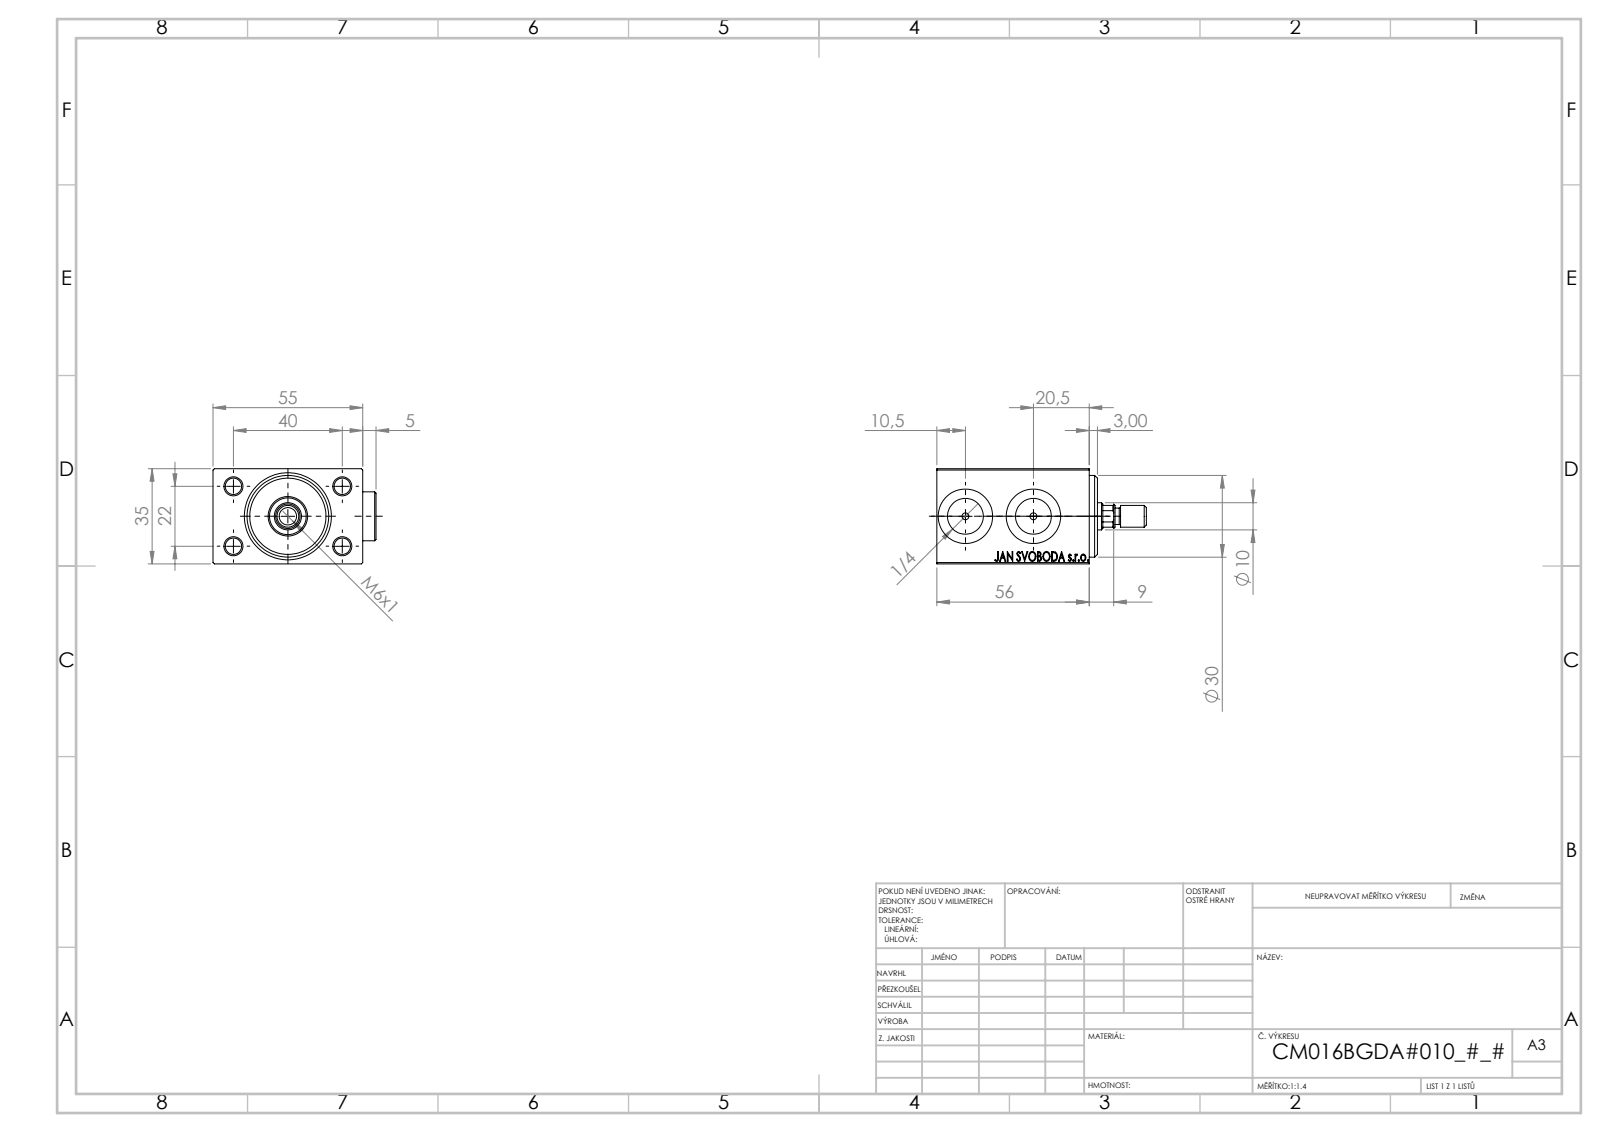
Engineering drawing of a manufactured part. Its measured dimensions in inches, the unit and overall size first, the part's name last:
Units: inches
Overall size (bounding box): 3.031 × 2.358 × 1.378
Round holes (diameter × count): ⌀0.236 ×4, ⌀0.098 ×2, ⌀0.518 ×2, ⌀0.787 ×2, ⌀0.177 ×1, ⌀0.394 ×1, ⌀0.531 ×1, ⌀0.571 ×1, ⌀0.63 ×1, ⌀0.709 ×1, ⌀1.181 ×1
Round bosses / shafts (diameter × count): ⌀0.709 ×2, ⌀0.315 ×1, ⌀0.236 ×1
Partial cylindrical surfaces — rounded edges, fillets, slot ends (radius × count): R0.177 ×1
Main face-to-face distances: 1.378, 0.197, 2.008, 2.165, 2.161, 2.205, 0.118, 0.315, 1.654, 2.323
Hole centre spacings: 0.899, 0.866, 1.575, 1.797, 0.984
Volume: 6.211 in³ · Surface area: 43.88 in²
Bodies: 6 solids, 949 faces (439 planar, 74 cylindrical, 436 other)
Part name (STEP PRODUCT): V450CM_B_Body; V450CM_VC_B; V450CM_MALE_METRIC; Zatka_OIL_PORT (+1 more)
STEP written by: SolidWorks 2019 (CONFIG_CONTROL_DESIGN)
